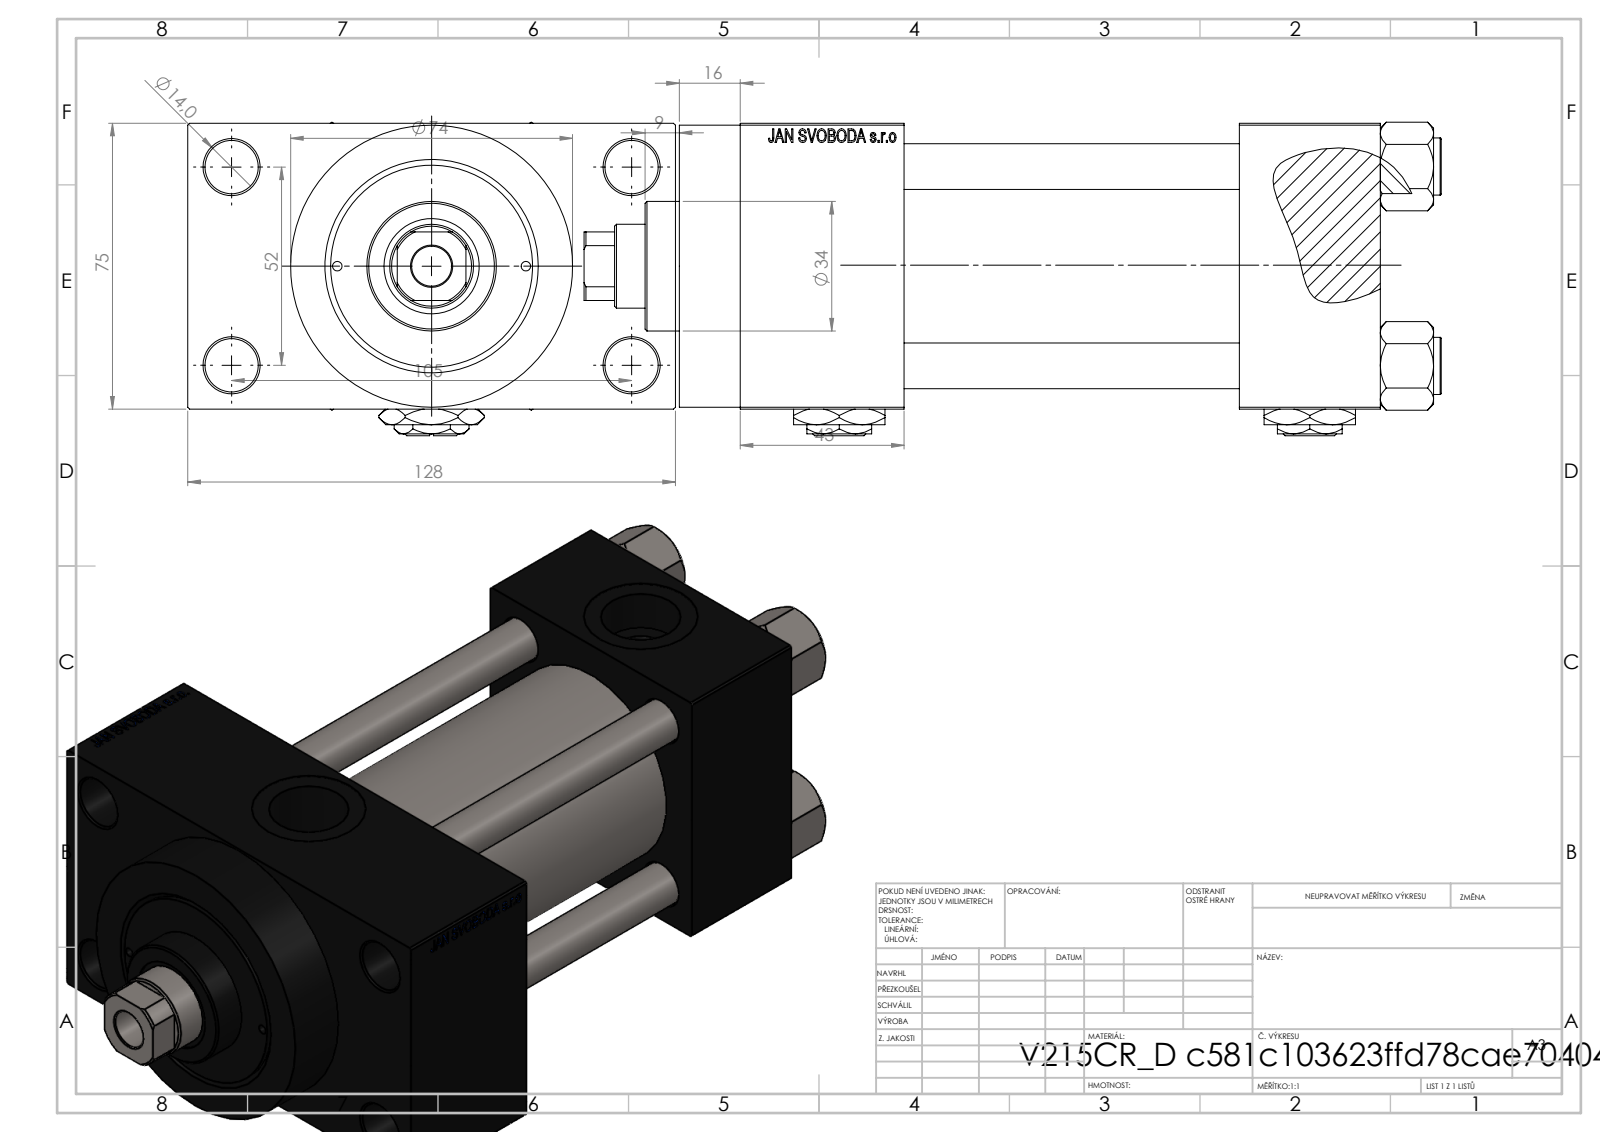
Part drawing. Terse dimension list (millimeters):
name: V215CR_VCP_D; V215_VC_A; NUT_M5_D; V215CR_D_TYCINKA (+2 more)
written by: SolidWorks 2019 (CONFIG_CONTROL_DESIGN)
unit: mm
bodies: 13 solids, 1213 faces (547 planar, 104 cylindrical, 562 other)
size: 225 × 128 × 82.27
volume: 841 898 mm³; area: 185 706 mm²
holes: 4× ⌀12, 4× ⌀14, 2× ⌀2.5, 2× ⌀7, 2× ⌀20.96, 2× ⌀30, 1× ⌀10.5, 1× ⌀22, 1× ⌀25, 1× ⌀41, 1× ⌀50, 1× ⌀53
bosses: 4× ⌀15, 1× ⌀74, 1× ⌀56, 1× ⌀34
rounds: 1× R10.5
face distances: 75, 88, 37, 125, 26.5, 101.5, 168, 131, 43, 16
hole spacings: 26.19, 26.35, 36.98, 38.03, 52.3, 57.22, 58.43, 58.59
